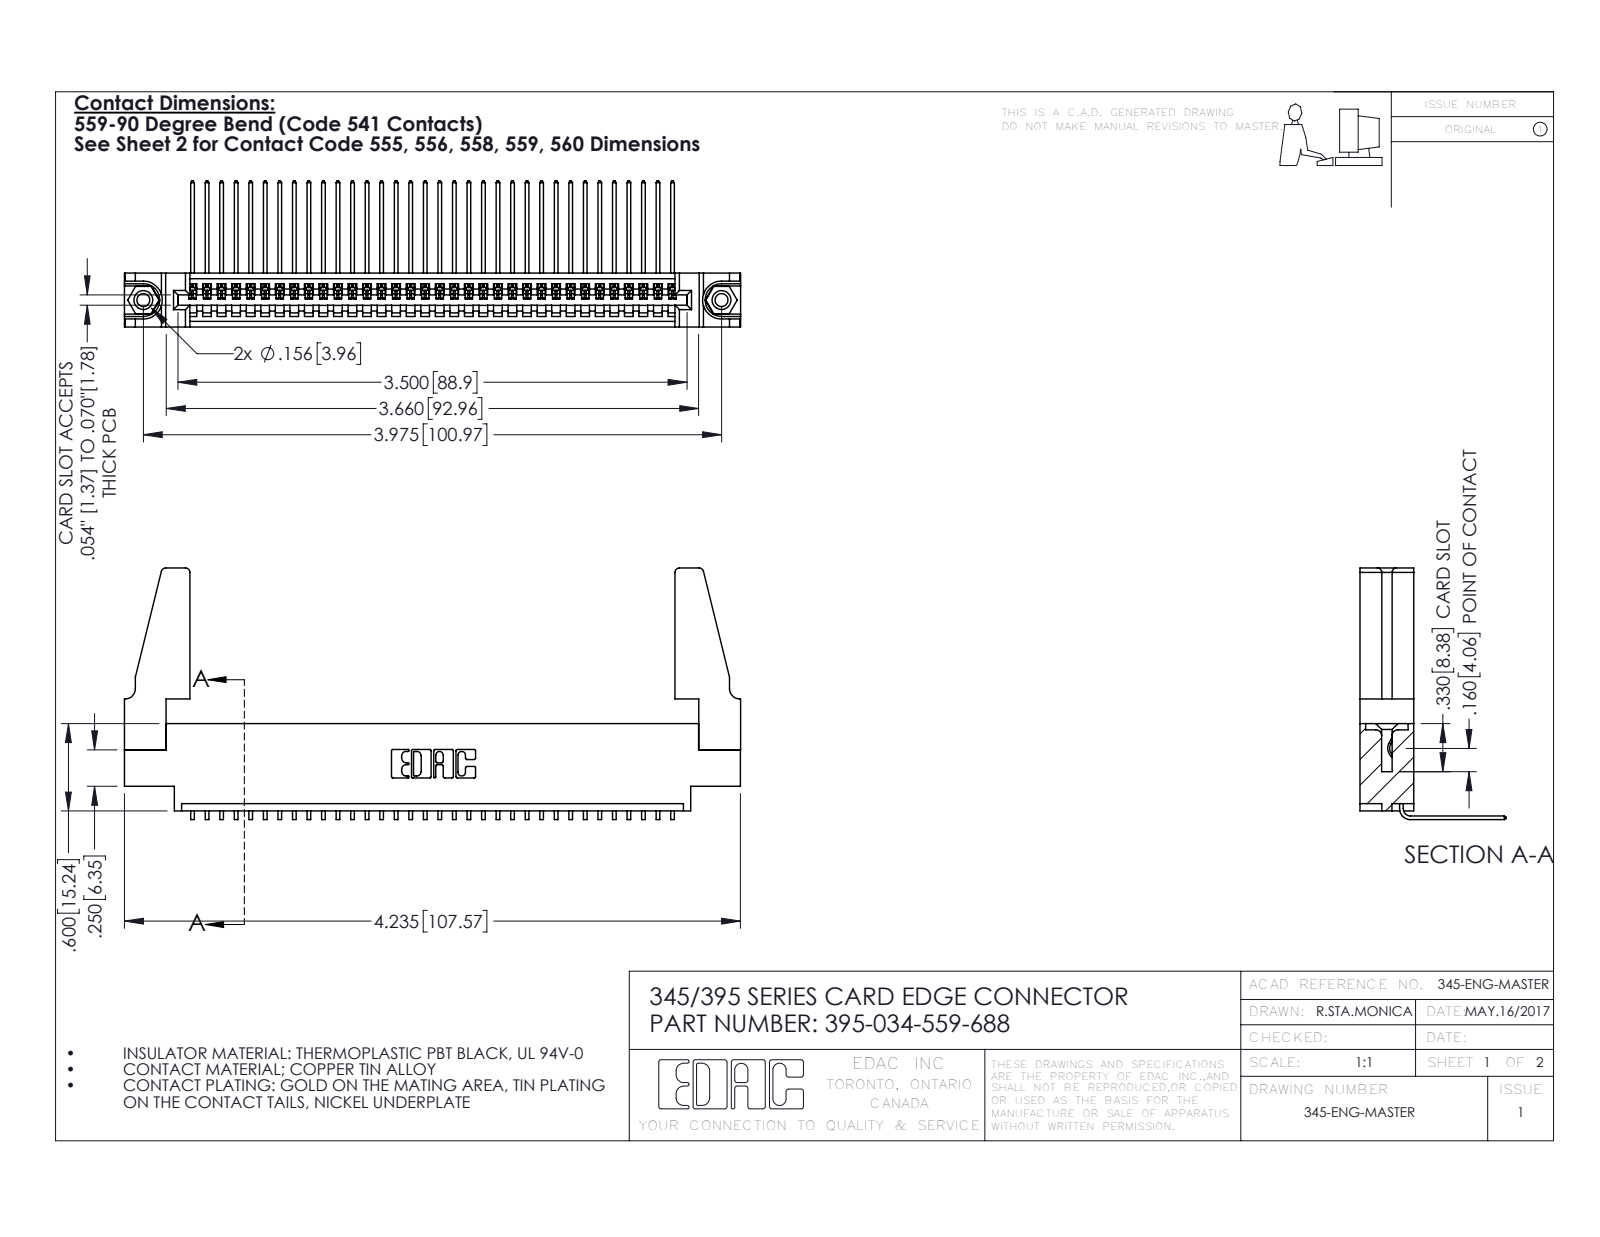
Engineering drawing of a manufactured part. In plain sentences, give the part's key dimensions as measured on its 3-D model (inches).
The part is named "345-250-001_345-250-001-102; 345 Part_0.170 Offset - 0.156 Dia-TH; 345-292-001_558 559 Tail - 1; 345-220-078_345-220-088 (+1 more)". Its 3-D file was written by "SolidWorks 2016 (CONFIG_CONTROL_DESIGN)". It is 39 solids with 2294 faces: 1584 planar, 694 cylindrical and 16 other. Overall it measures 4.236 by 1.729 by 1.005 inches. Its volume is 0.818 cubic inches and its surface area 26.82 square inches. Round holes: 2 of diameter 0.089, 2 of diameter 0.125, 2 of diameter 0.156, 1 of diameter 0.064. Round bosses or shafts: 2 of diameter 0.155. Partial cylindrical surfaces (rounded edges, fillets, slot ends): 68 of radius 0.006, 22 of radius 0.01, 8 of radius 0.03, 6 of radius 0.007, 6 of radius 0.031, 3 of radius 0.026, 2 of radius 0.031, 2 of radius 0.04. The main face-to-face distances are 0.37, 0.072, 0.298, 0.2, 0.098, 0.272, 0.025, 0.225, 0.175, 0.149. The hole center spacings are 0.27, 3.74, 3.975.
